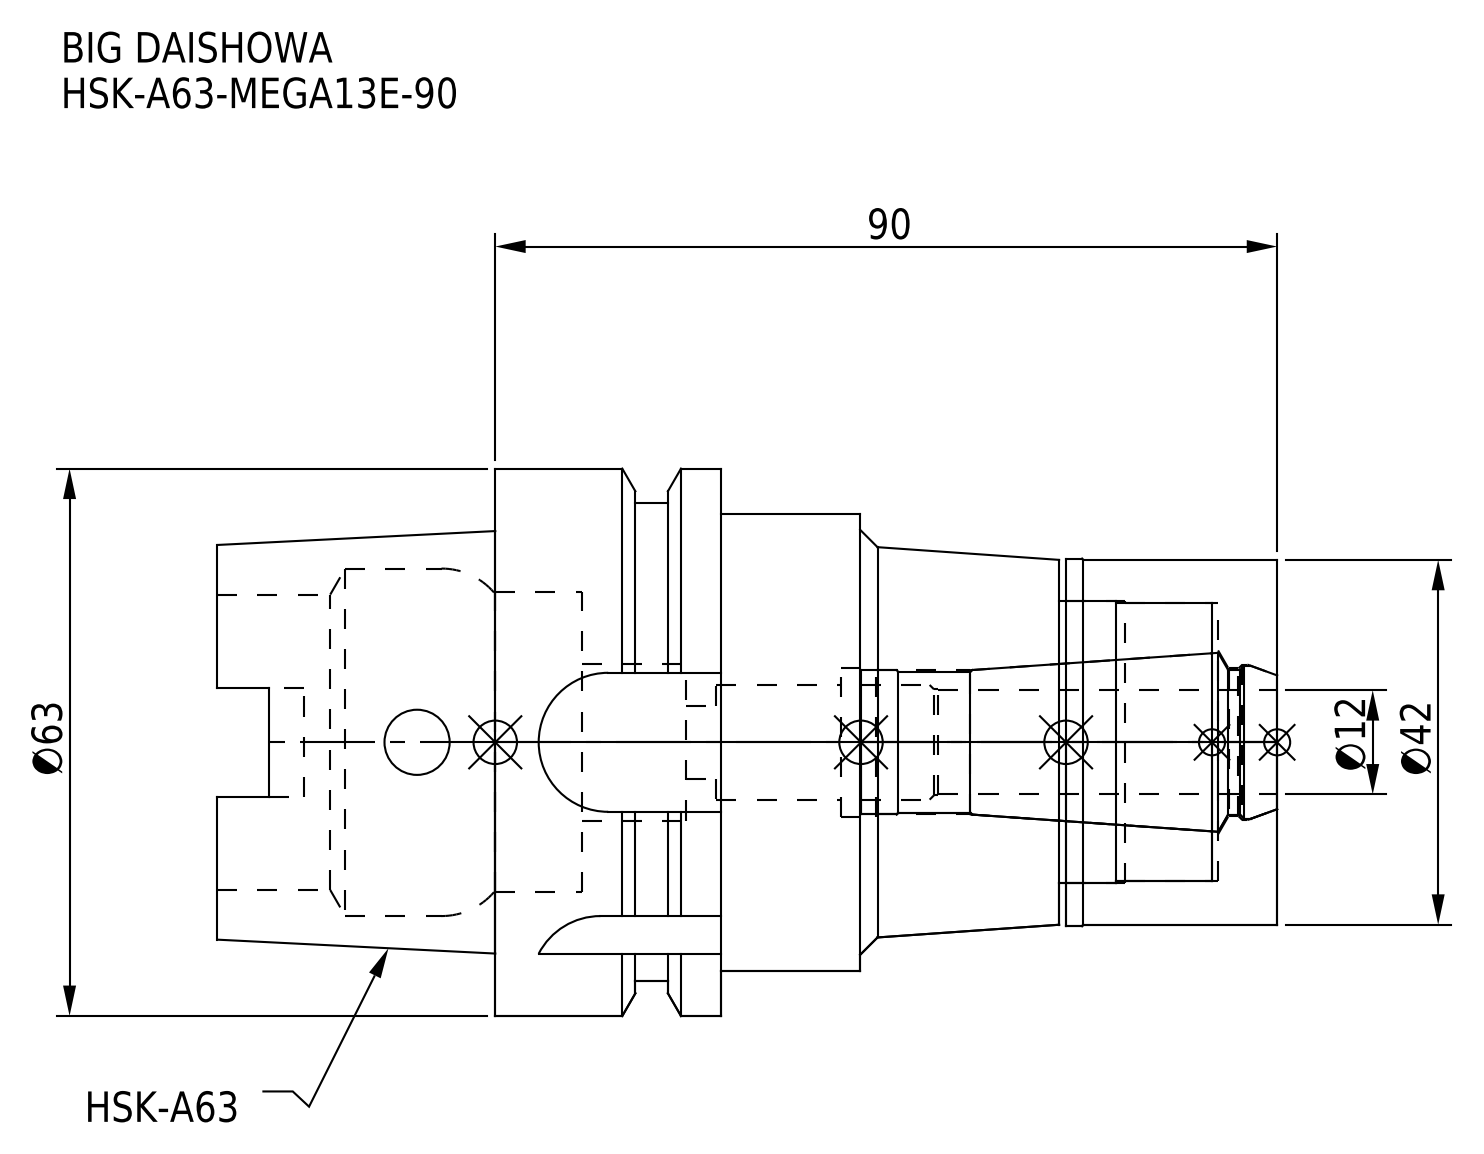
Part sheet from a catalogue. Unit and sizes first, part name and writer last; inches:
Units: inches
Overall size (bounding box): 4.803 × 2.48 × 2.48
Round holes (diameter × count): ⌀0.295 ×1, ⌀0.331 ×1, ⌀0.524 ×1, ⌀0.654 ×1, ⌀0.669 ×1, ⌀0.677 ×1, ⌀0.705 ×1, ⌀0.709 ×1, ⌀1.26 ×1, ⌀1.28 ×1, ⌀1.339 ×1, ⌀1.358 ×1
Round bosses / shafts (diameter × count): ⌀2.48 ×1, ⌀2.165 ×1, ⌀2.071 ×1, ⌀1.665 ×1, ⌀1.654 ×1
Partial cylindrical surfaces — rounded edges, fillets, slot ends (radius × count): R0.11 ×2, R0.113 ×2, R0.315 ×2, R0.354 ×1
Main face-to-face distances: 3.543, 2.52, 1.024, 3.152, 0.632, 0.392, 0.988, 0.957, 1.563, 2.195
Volume: 10.39 in³ · Surface area: 62.21 in²
Bodies: 2 solids, 127 faces (45 planar, 54 cylindrical, 28 other)
Part name (STEP PRODUCT): HSK-A63-MEGA13E-90_1.stp; MEN13_1.stp; HA63ME13090-120_ASM.stp; HSK-A63-MEGA13E-90-120-FreeParts (+3 more)
STEP written by: SolidWorks 2019 (CONFIG_CONTROL_DESIGN)
